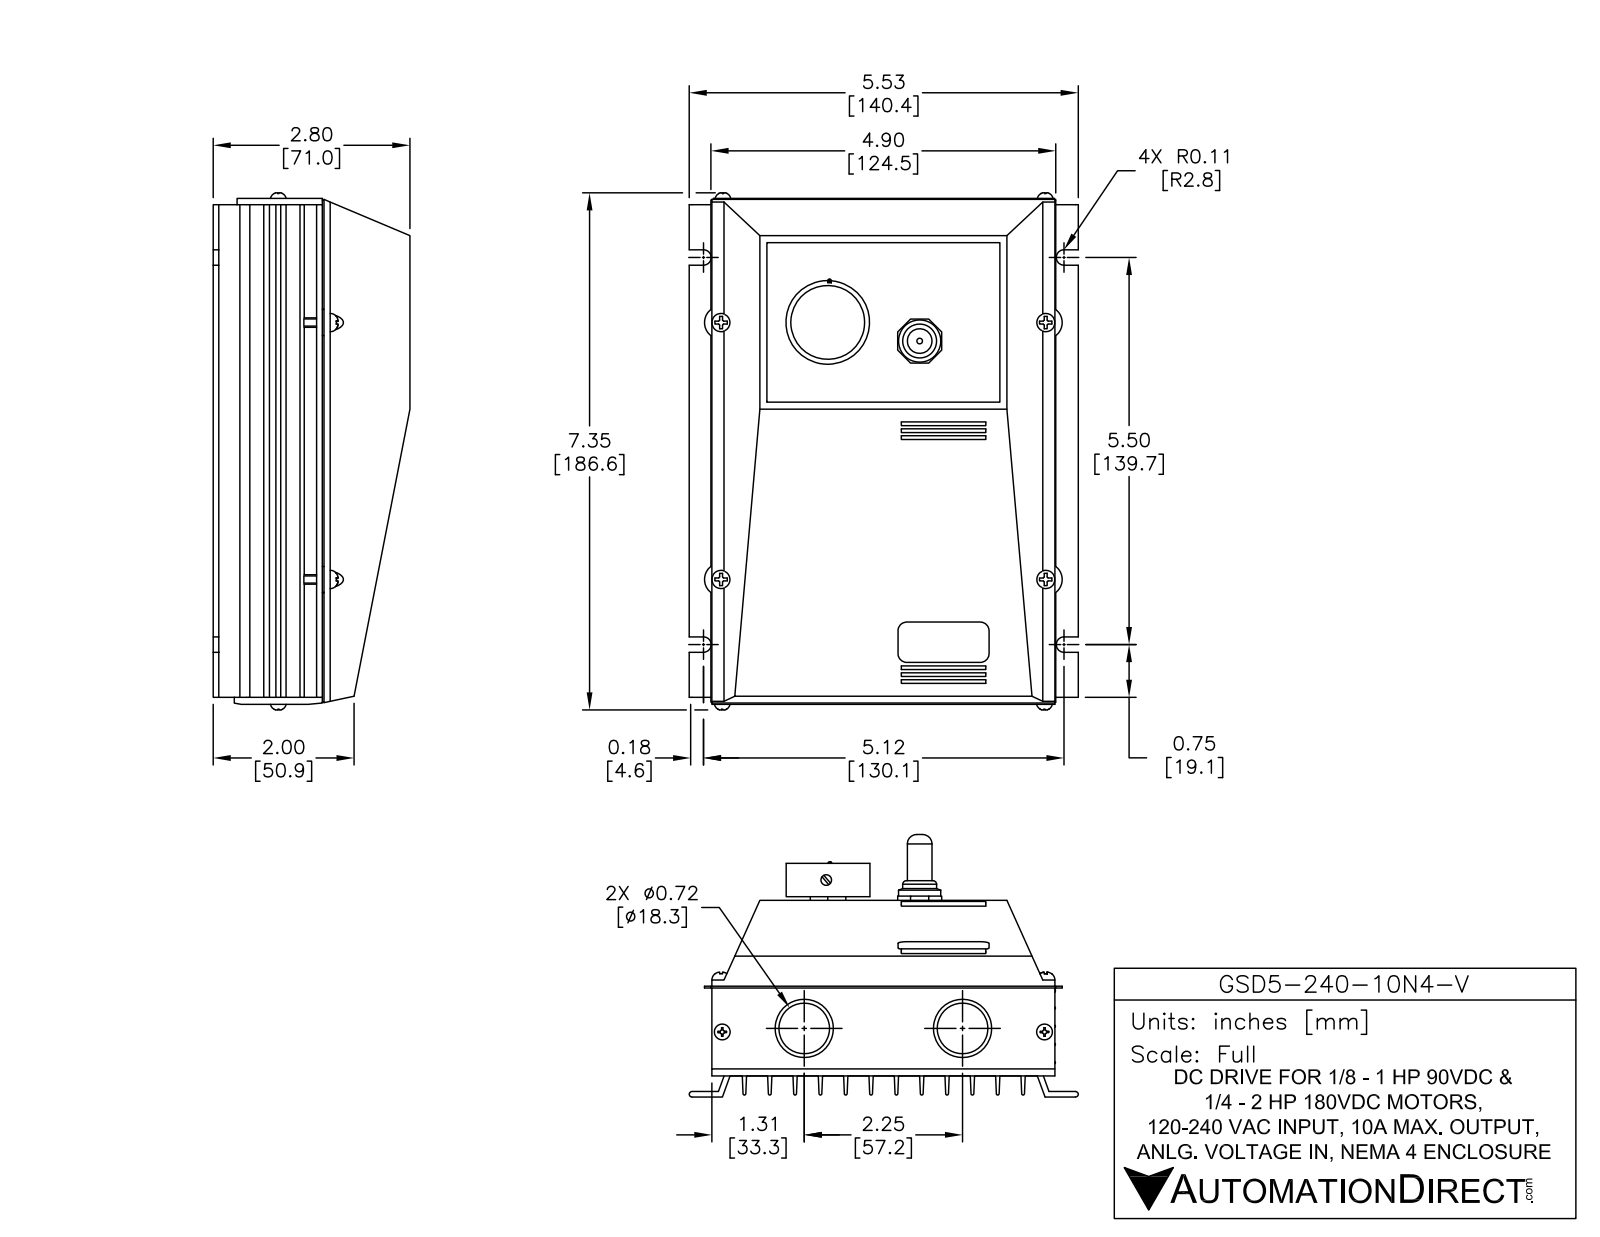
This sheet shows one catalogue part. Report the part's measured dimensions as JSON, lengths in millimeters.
{"part_name": "PT250KWO_1; PC250G_1; SW250SEAL - NUT ASSEMBLY_1; EP250WH_1 (+8 more)", "step_written_by": "SolidWorks 2014 (AUTOMOTIVE_DESIGN)", "units": "millimeters", "bodies": {"solids": 26, "faces": 2622, "planar": 1879, "cylindrical": 624, "other": 119}, "overall_size": [186.6, 140.4, 91.2], "volume_mm3": 321400, "surface_area_mm2": 304200, "round_holes": [[3.6, 11], [7, 5], [2.9, 4], [1.9, 3], [2.4, 3], [2.6, 3], [18.3, 2], [33.5, 2], [1.5, 1], [3.8, 1], [9.5, 1], [9.7, 1]], "round_bosses_or_shafts": [[6, 11], [3.6, 11], [1.7, 7], [4.4, 5], [3.4, 4], [3.3, 4], [2.8, 4], [1.7, 4]], "partial_cylinders_radius": [[0.6, 92], [0.5, 19], [1.3, 16], [9.9, 11], [12.3, 11], [0.5, 8], [3.2, 8], [0.8, 6]], "face_to_face_distances": [2.5, 18.3, 2, 36.6, 60.2, 9.1, 11.6, 54.8, 10.1, 7.5], "hole_center_spacings": [92.7, 116.9, 117.2, 117.2, 149.2, 149.4, 21.1, 63.4]}
